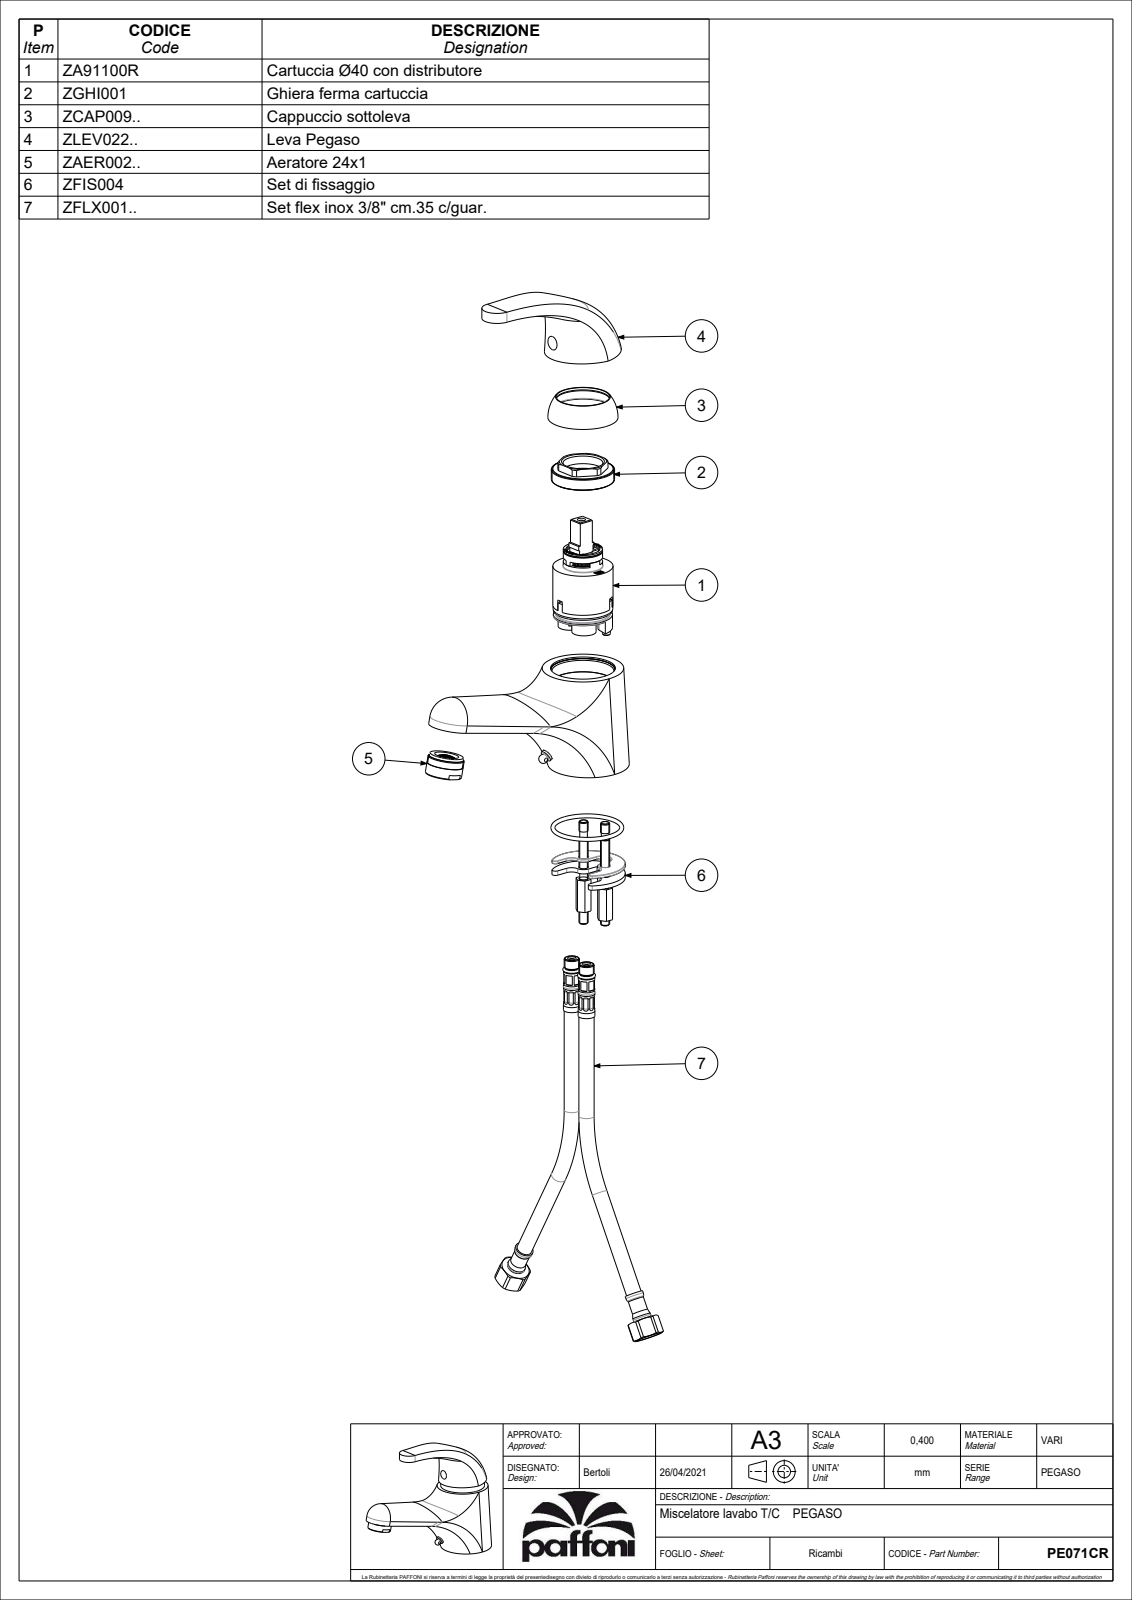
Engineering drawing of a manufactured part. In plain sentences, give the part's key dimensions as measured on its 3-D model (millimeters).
The part is named "PE071CR_SW0001". Its 3-D file was written by "CREO PARAMETRIC BY PTC INC, 2022124 (CONFIG_CONTROL_DESIGN)". It is 3 solids with 2417 faces: 1929 planar, 232 cylindrical and 256 other. Overall it measures 158.92 by 122.07 by 53.5 millimeters. Its volume is 148 267 cubic millimeters and its surface area 86 194 square millimeters. Round holes: 4 of diameter 8, 3 of diameter 11, 2 of diameter 5.5, 2 of diameter 7, 2 of diameter 9, 2 of diameter 12, 1 of diameter 4, 1 of diameter 5, 1 of diameter 6, 1 of diameter 15, 1 of diameter 16, 1 of diameter 17. Round bosses or shafts: 2 of diameter 15.9, 2 of diameter 10, 2 of diameter 9.4, 2 of diameter 8, 1 of diameter 42, 1 of diameter 39.2, 1 of diameter 38.8, 1 of diameter 34.8. Partial cylindrical surfaces (rounded edges, fillets, slot ends): 44 of radius 0.5, 8 of radius 1, 6 of radius 1.5, 4 of radius 0.3, 4 of radius 7.5, 2 of radius 2, 2 of radius 5.5, 2 of radius 6.5. The main face-to-face distances are 3.5, 6, 3, 4, 21, 2, 15.5, 22, 12, 0.5. The hole center spacings are 1.12, 9.9, 13.04, 14.53, 2, 8.6, 9.6, 10.97.
